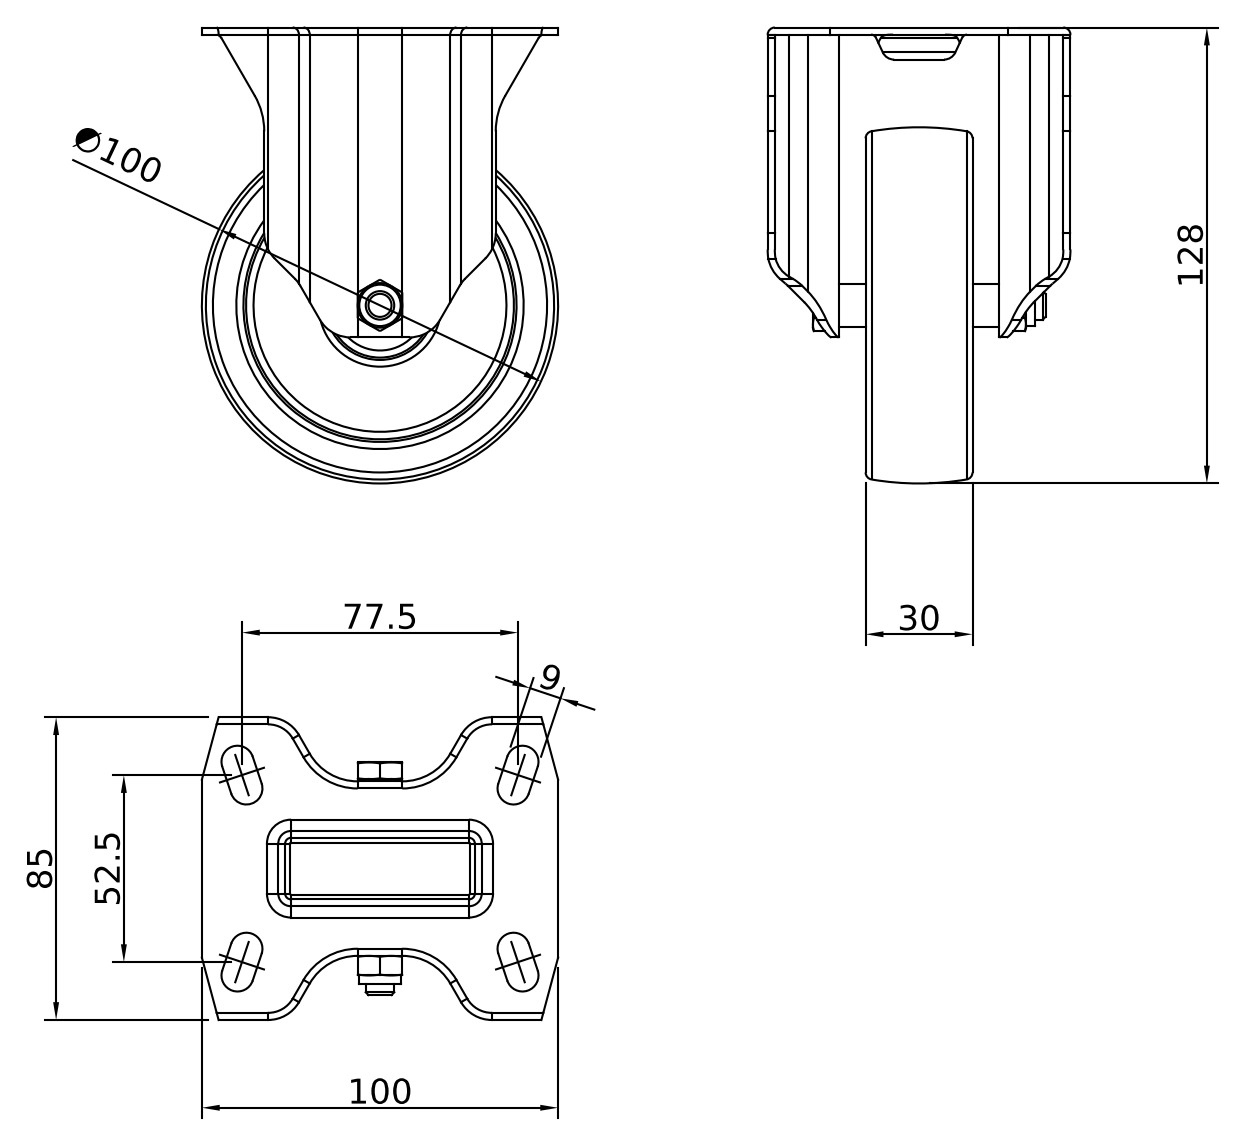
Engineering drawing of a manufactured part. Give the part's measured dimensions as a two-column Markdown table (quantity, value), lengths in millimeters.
| quantity | value |
| --- | --- |
| part name | CRUST0000003 |
| STEP written by | Autodesk Inventor 2022 (AUTOMOTIVE_DESIGN) |
| units | millimeters |
| bodies | 1 solid, 238 faces (93 planar, 83 cylindrical, 62 other) |
| overall size | 128 × 100 × 85 |
| volume | 183 109 mm³ |
| surface area | 72 332 mm² |
| round holes (diameter × count) | 12 × 1 |
| round bosses / shafts (diameter × count) | 11.63 × 1, 8 × 1 |
| partial cylindrical surfaces (radius × count) | 2 × 10, 10 × 10, 1.5 × 8, 3.5 × 8, 4.5 × 8, 7 × 4, 8 × 4, 15.5 × 4 |
| main face-to-face distances | 2, 30, 7.5, 37.5, 9.5, 39.5, 47, 65, 3.92, 18 |
